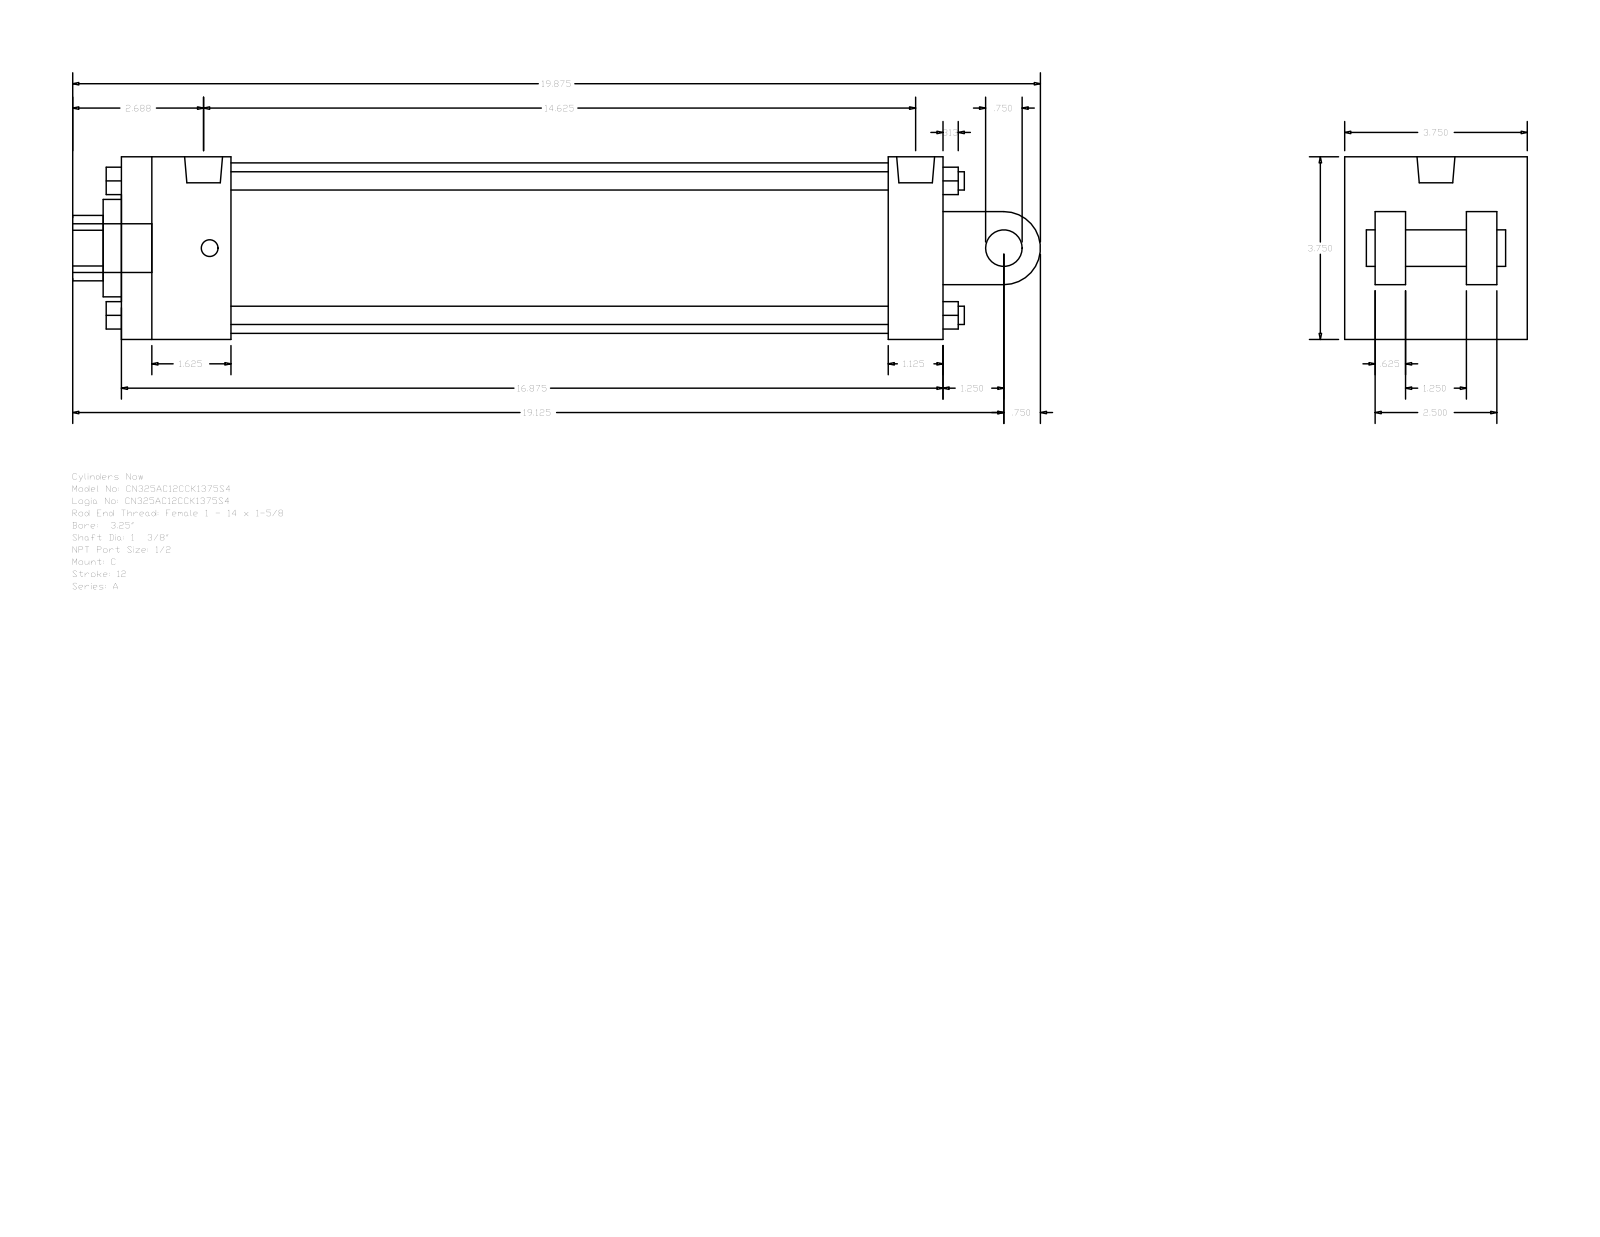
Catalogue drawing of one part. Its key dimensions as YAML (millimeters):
part_name: "A_C__0325_1.375"
step_written_by: "GSSL Pune (CONFIG_CONTROL_DESIGN)"
units: millimeters
bodies: {solids: 0, faces: 135, planar: 102, cylindrical: 33, other: 0}
overall_size: [504.82, 95.25, 95.25]
round_holes:
  - {diameter: 8.73, count: 2}
  - {diameter: 19.77, count: 1}
  - {diameter: 34.92, count: 1}
  - {diameter: 50.8, count: 1}
  - {diameter: 88.9, count: 1}
round_bosses_or_shafts:
  - {diameter: 9.53, count: 4}
  - {diameter: 8.73, count: 2}
  - {diameter: 25.4, count: 1}
  - {diameter: 19.77, count: 1}
  - {diameter: 19.05, count: 1}
partial_cylinders:
  - {radius: 17.06, count: 1}
  - {radius: 19.05, count: 1}
face_to_face_distances: [95.24, 15.87, 428.62, 28.57, 63.5, 66.67, 79.37, 31.74, 47.63, 400.05]
hole_center_spacings: [3.18]
